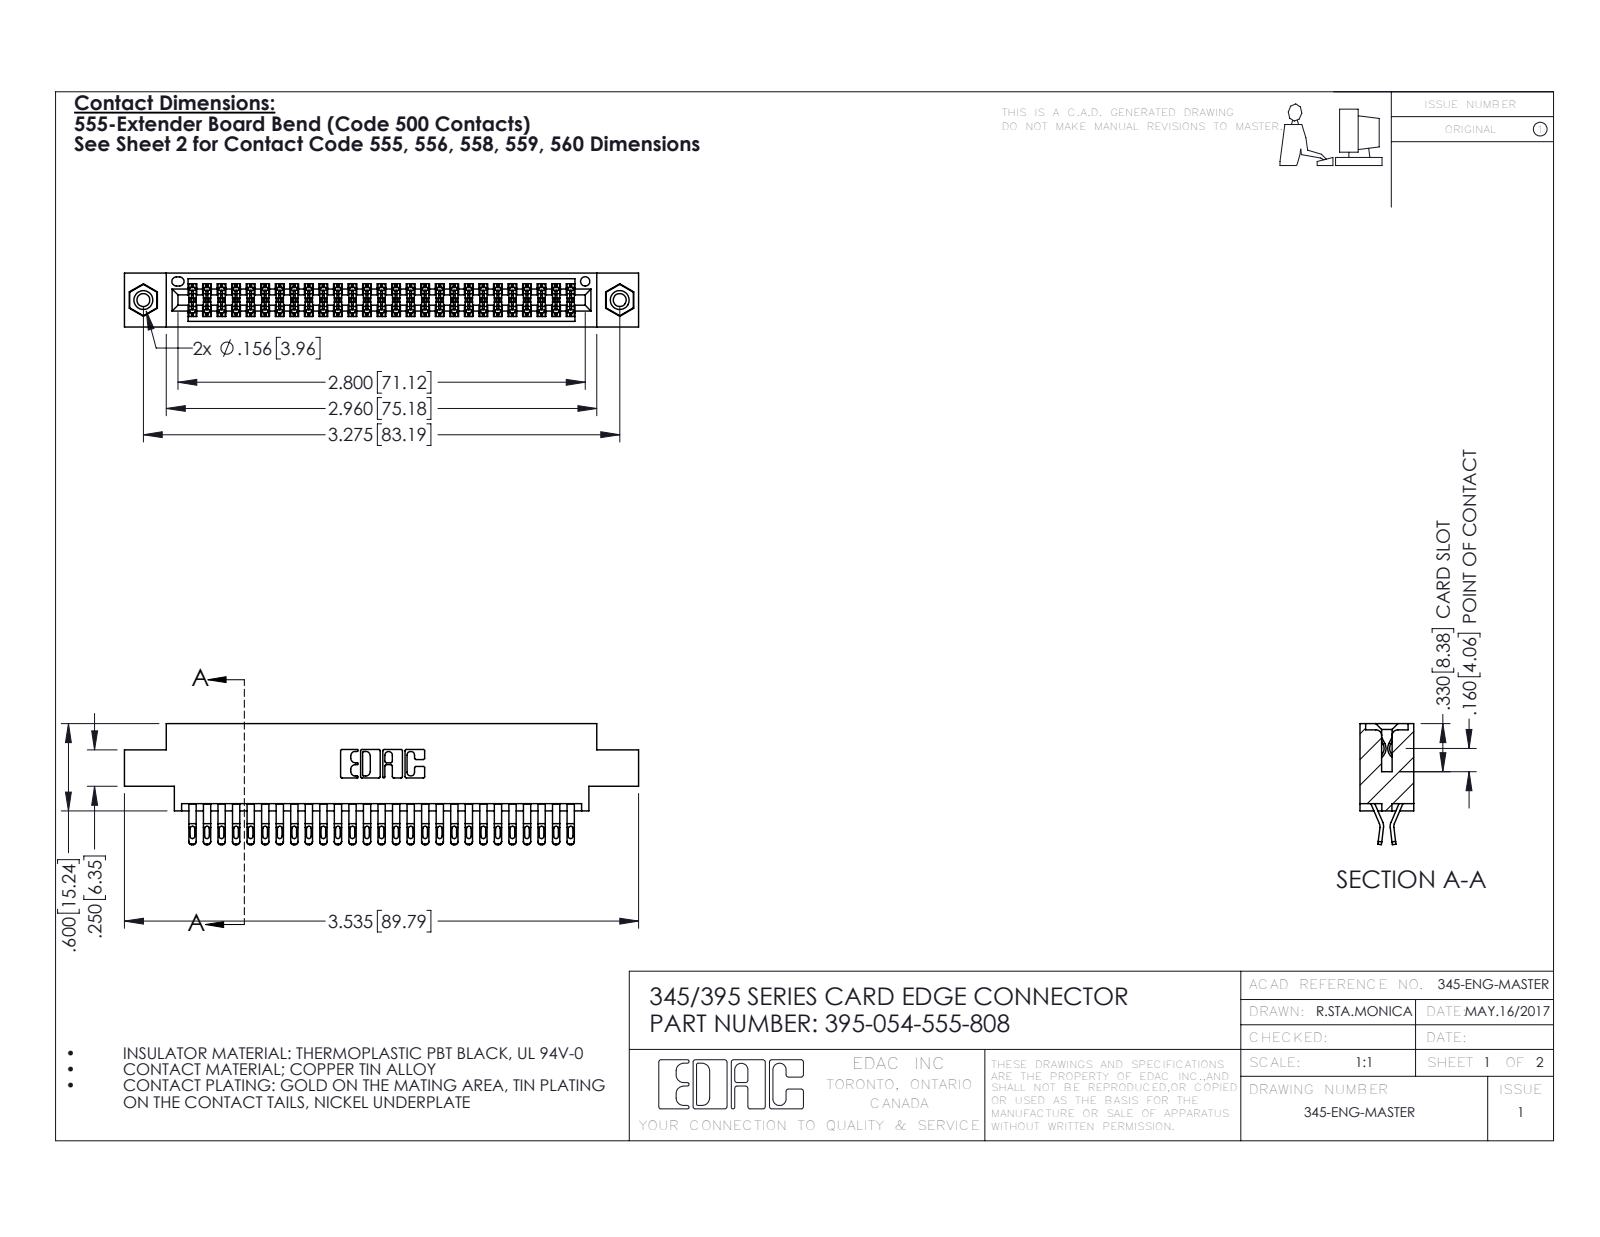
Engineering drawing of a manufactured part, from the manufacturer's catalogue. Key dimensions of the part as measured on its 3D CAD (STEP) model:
Part name (STEP PRODUCT): 345-292-001_555 Tail; 345-250-001_345-250-003-102; 345 Part_0.170 Offset - 0.156 Dia-TI; 395-054-555-808
STEP written by: SolidWorks 2016 (CONFIG_CONTROL_DESIGN)
Units: inches
Bodies: 57 solids, 3214 faces (1790 planar, 1408 cylindrical, 16 other)
Overall size (bounding box): 3.535 × 0.832 × 0.37
Volume: 0.526 in³ · Surface area: 20.39 in²
Round holes (diameter × count): ⌀0.089 ×2, ⌀0.125 ×2, ⌀0.156 ×2, ⌀0.064 ×1
Round bosses / shafts (diameter × count): ⌀0.155 ×2
Partial cylindrical surfaces — rounded edges, fillets, slot ends (radius × count): R0.016 ×135, R0.02 ×108, R0.006 ×81, R0.01 ×22, R0.007 ×6, R0.031 ×6, R0.026 ×3, R0.01 ×2
Main face-to-face distances: 0.072, 0.298, 0.37, 0.025, 0.2, 0.098, 0.272, 0.225, 0.175, 0.149
Hole centre spacings: 0.27, 3.04, 3.275
